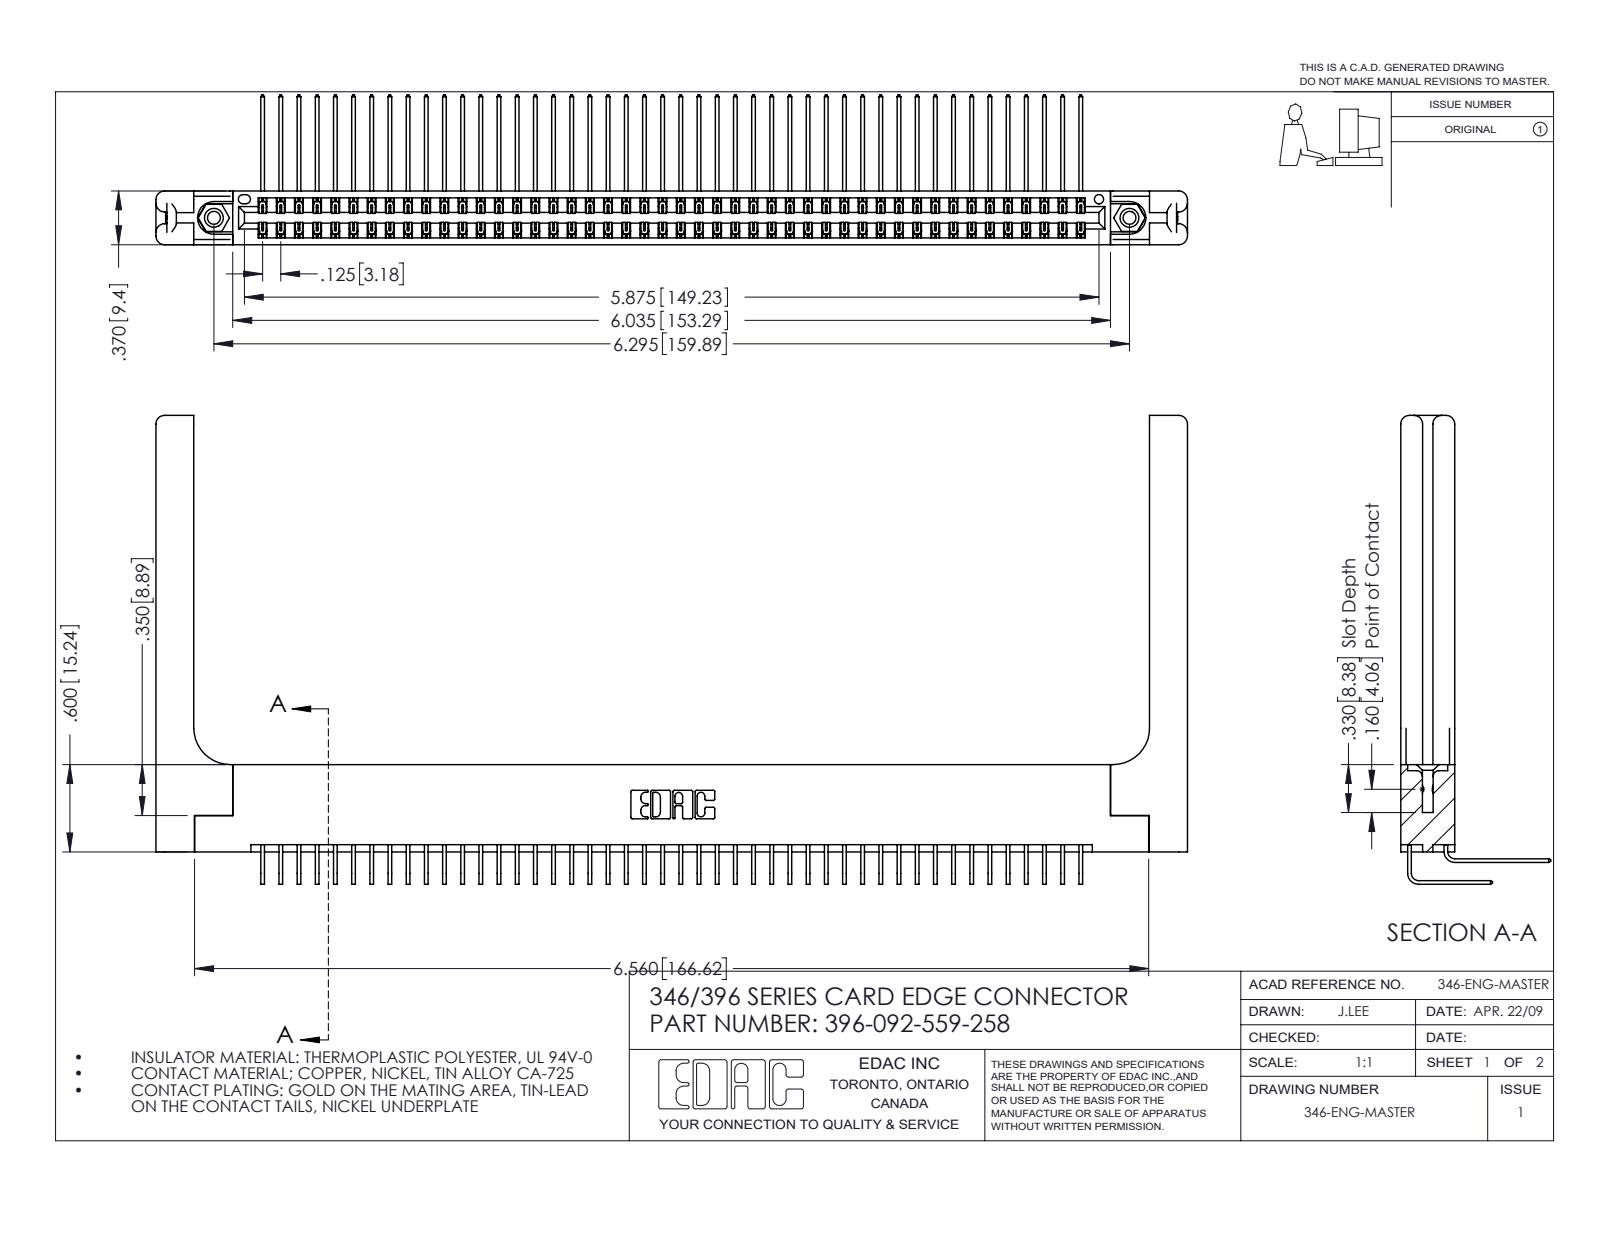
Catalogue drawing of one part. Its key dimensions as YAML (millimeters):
part_name: "345-292-001_558 559 Tail - 1; 396-092-559-258; 346 Part_Flush Mounting Lugs - 0.156 Dia-TH; 345-292-001_559 Tail - 2 (+2 more)"
step_written_by: "SolidWorks 2016 (CONFIG_CONTROL_DESIGN)"
units: millimeters
bodies: {solids: 97, faces: 5346, planar: 3628, cylindrical: 1658, other: 60}
overall_size: [180.1, 81.9, 26.2]
volume: 25610
surface_area: 32500
round_holes:
  - {diameter: 2.3, count: 2}
  - {diameter: 3.2, count: 2}
  - {diameter: 4, count: 2}
  - {diameter: 1.6, count: 1}
round_bosses_or_shafts:
  - {diameter: 3.9, count: 2}
partial_cylinders:
  - {radius: 0.2, count: 138}
  - {radius: 0.3, count: 22}
  - {radius: 1.5, count: 16}
  - {radius: 0.2, count: 6}
  - {radius: 0.8, count: 6}
  - {radius: 0.7, count: 3}
  - {radius: 0.4, count: 2}
  - {radius: 0.6, count: 2}
face_to_face_distances: [1.2, 8.2, 9.4, 1.8, 0.6, 6.4, 3.8, 3.8, 7.6, 7]
hole_center_spacings: [6.2, 154.6, 159.9]
